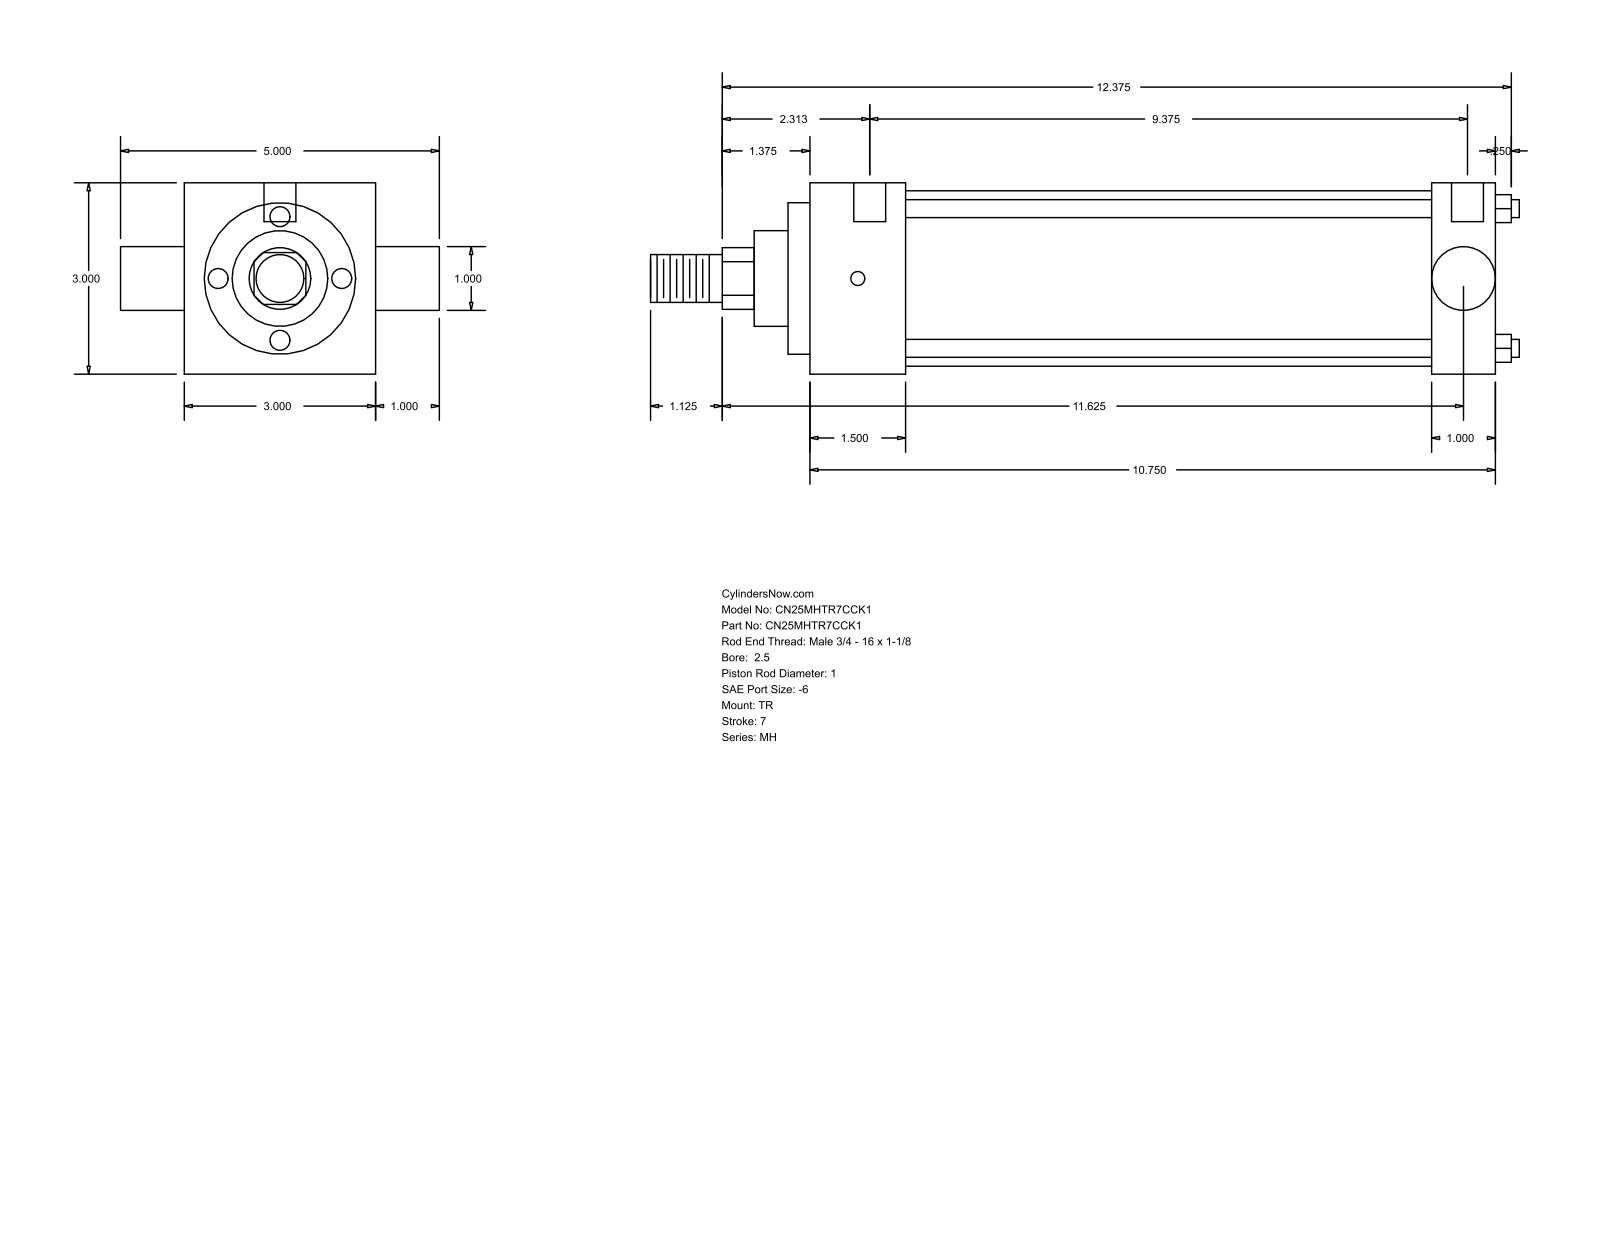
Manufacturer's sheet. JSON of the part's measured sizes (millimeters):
{"part_name": "MH_TR__0250_1", "step_written_by": "GSSL Pune (CONFIG_CONTROL_DESIGN)", "units": "millimeters", "bodies": {"solids": 0, "faces": 86, "planar": 61, "cylindrical": 25, "other": 0}, "overall_size": [346.07, 127, 76.2], "round_holes": [[5.56, 3], [12.7, 2]], "round_bosses_or_shafts": [[7.14, 4], [69.85, 1], [60.33, 1], [38.1, 1], [25.4, 1], [25.35, 1], [19.05, 1]], "partial_cylinders_radius": [[12.29, 1]], "face_to_face_distances": [76.2, 273.06, 38.11, 234.95, 247.65, 209.54, 25.41, 8.73, 46.84, 256.38], "hole_center_spacings": [3.18, 4.76, 238.12, 241.3, 242.88, 246.06]}
